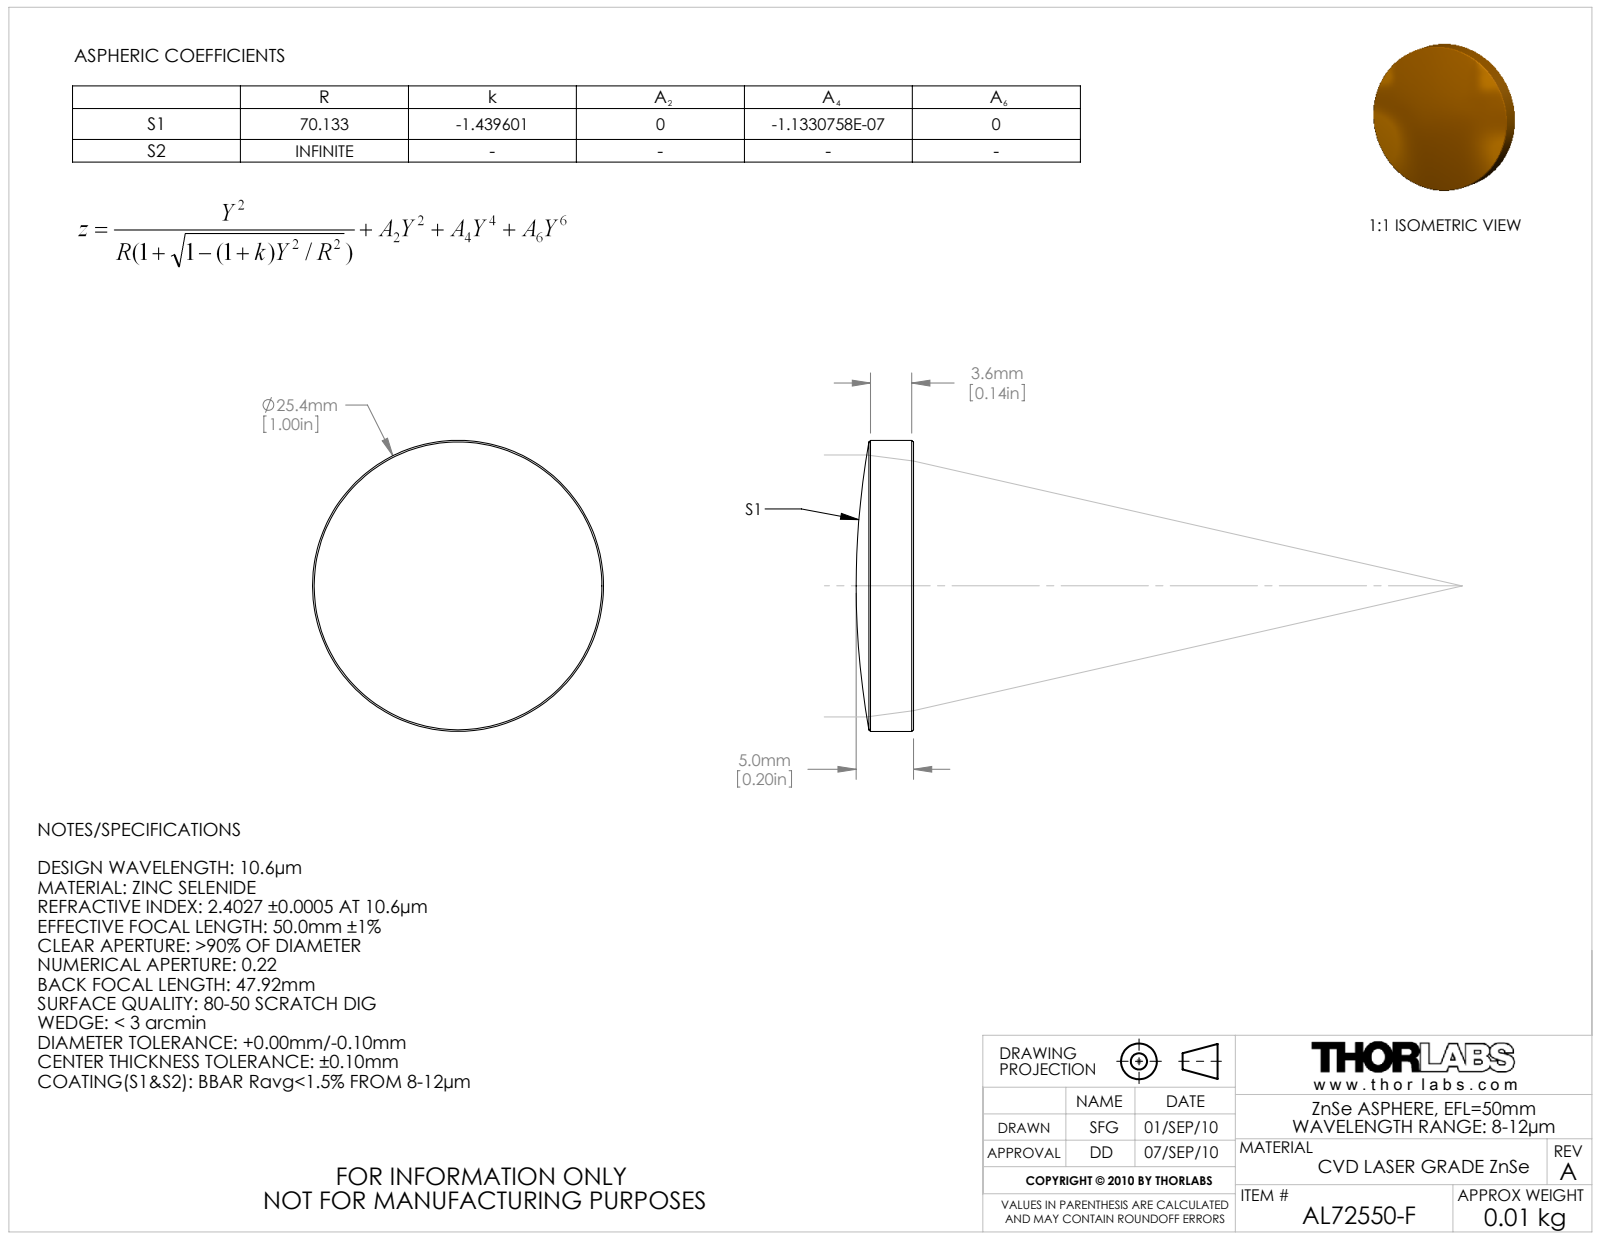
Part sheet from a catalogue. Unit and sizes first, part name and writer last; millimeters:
Units: millimetres
Overall size (bounding box): 25.4 × 25.4 × 5
Round bosses / shafts (diameter × count): ⌀25.4 ×1
Volume: 2 250 mm³ · Surface area: 1 314 mm²
Bodies: 1 solid, 9 faces (1 planar, 2 cylindrical, 6 other)
Part name (STEP PRODUCT): 21488-E0W
STEP written by: SolidWorks 2009 (AUTOMOTIVE_DESIGN)
